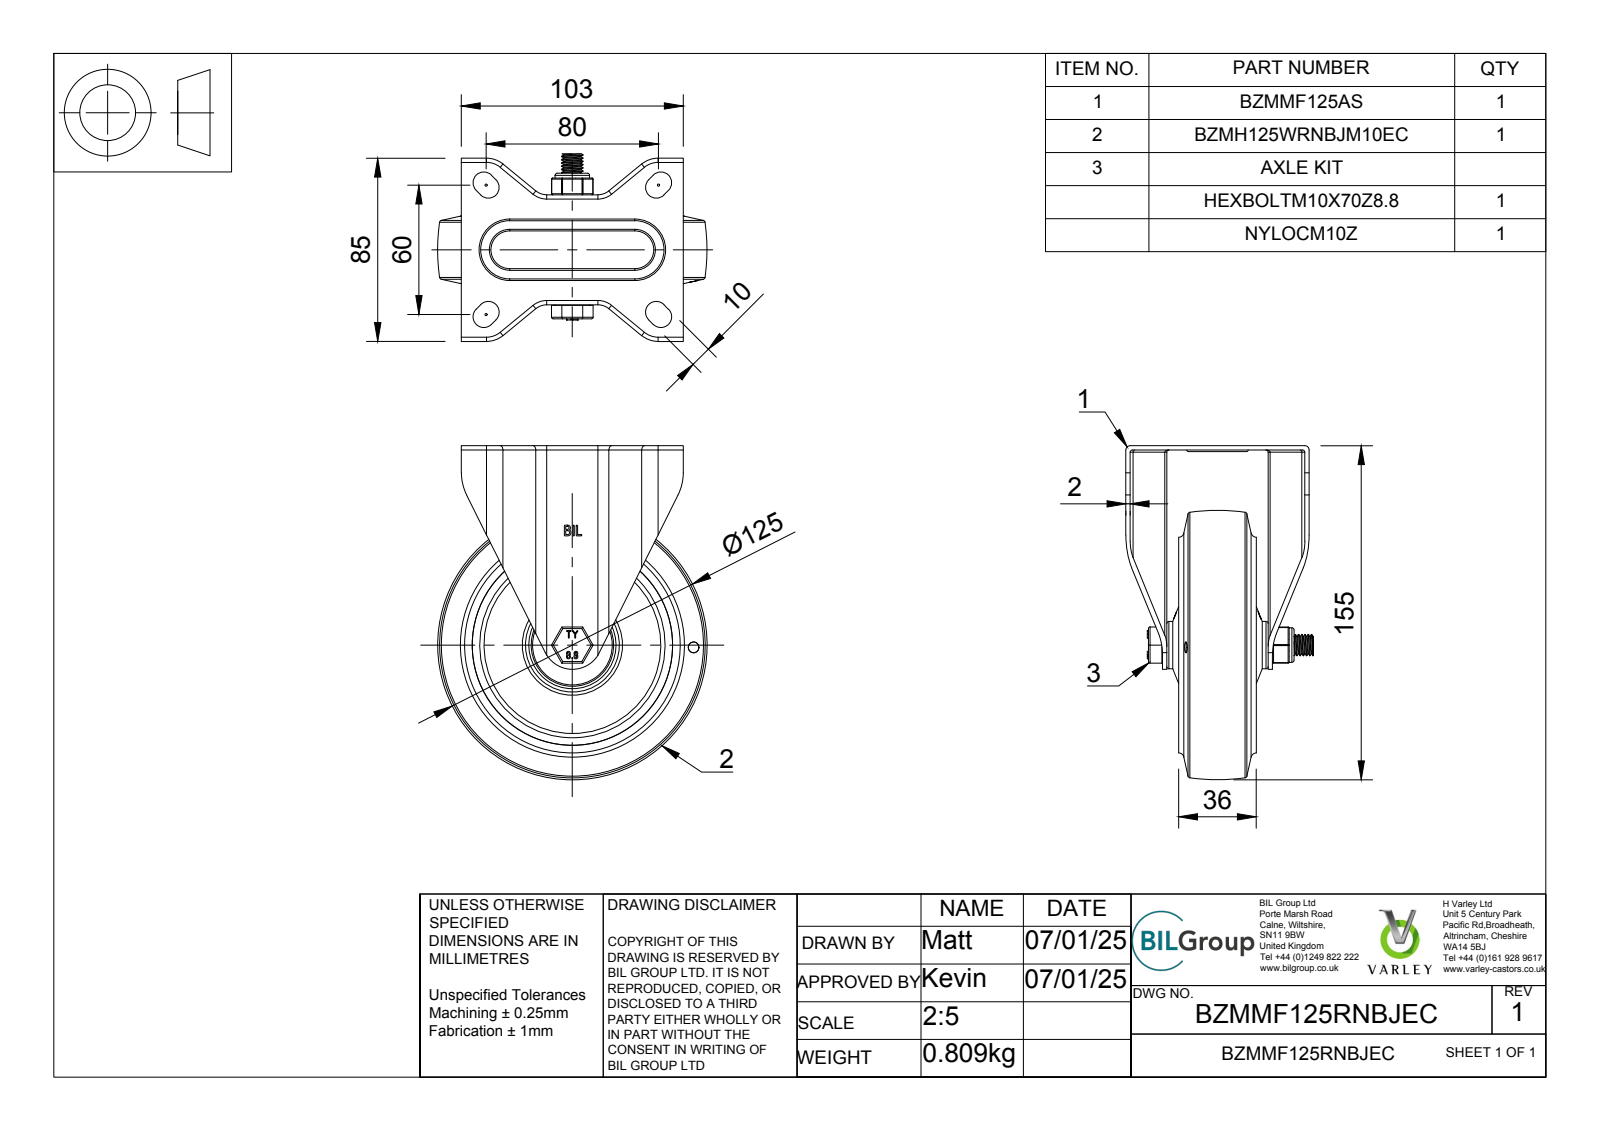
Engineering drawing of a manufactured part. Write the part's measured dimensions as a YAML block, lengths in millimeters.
part_name: "BZMMF125RNBJEC v3; BZMH125WRNBJM10EC v1; BZMM125WRNBJEC; 65 SHORE A ELASTIC RUBBER TYRE (+7 more)"
step_written_by: "Autodesk Translation Framework v13.20.0.188 (AP242_MANAGED_MODEL_BASED_3D_ENGINEERING_MIM_LF)"
units: millimeters
bodies: {solids: 24, faces: 776, planar: 292, cylindrical: 205, other: 279}
overall_size: [155, 125, 87]
volume: 304474
surface_area: 143350
round_holes:
  - {diameter: 4, count: 2}
  - {diameter: 5, count: 1}
  - {diameter: 10, count: 1}
  - {diameter: 10.2, count: 1}
  - {diameter: 12, count: 1}
  - {diameter: 15, count: 1}
  - {diameter: 20, count: 1}
  - {diameter: 22.5, count: 1}
  - {diameter: 25.5, count: 1}
  - {diameter: 30, count: 1}
  - {diameter: 31, count: 1}
  - {diameter: 32, count: 1}
round_bosses_or_shafts:
  - {diameter: 43.5, count: 1}
  - {diameter: 38.25, count: 1}
  - {diameter: 34.5, count: 1}
  - {diameter: 30.5, count: 1}
  - {diameter: 28, count: 1}
  - {diameter: 23, count: 1}
  - {diameter: 22, count: 1}
  - {diameter: 19.5, count: 1}
partial_cylinders:
  - {radius: 0.5, count: 18}
  - {radius: 0.75, count: 14}
  - {radius: 1, count: 8}
  - {radius: 2, count: 8}
  - {radius: 5, count: 8}
  - {radius: 12, count: 5}
  - {radius: 4, count: 4}
  - {radius: 6, count: 4}
face_to_face_distances: [2, 7.5, 23.5, 21.5, 25.5, 18.84, 20, 16, 27.5, 49]
